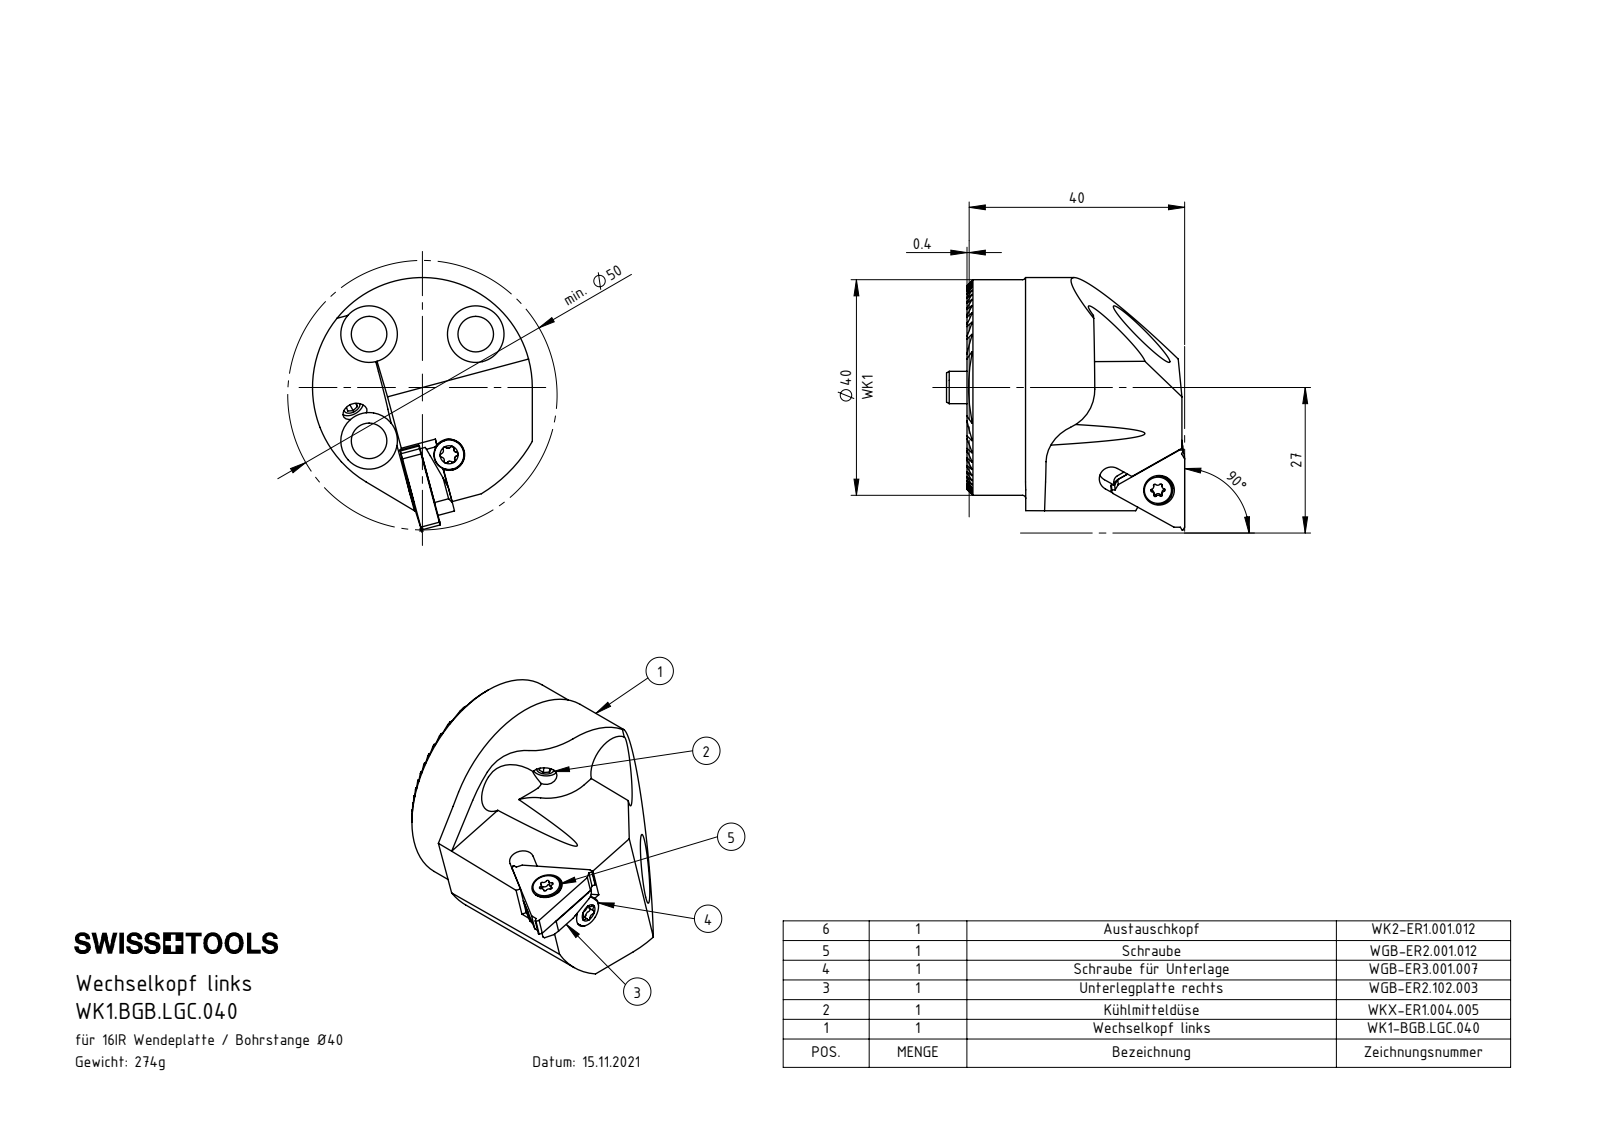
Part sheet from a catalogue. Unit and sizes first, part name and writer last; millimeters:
Units: millimetres
Overall size (bounding box): 47.42 × 44.27 × 42
Round holes (diameter × count): ⌀6.6 ×3, ⌀10.5 ×3, ⌀2.58 ×2, ⌀3.3 ×2, ⌀4 ×2, ⌀1.7 ×1, ⌀3 ×1, ⌀4.02 ×1, ⌀4.2 ×1, ⌀4.5 ×1, ⌀12 ×1
Round bosses / shafts (diameter × count): ⌀5.5 ×2, ⌀4 ×2, ⌀40 ×1, ⌀6 ×1, ⌀3.18 ×1, ⌀3 ×1, ⌀2.78 ×1
Partial cylindrical surfaces — rounded edges, fillets, slot ends (radius × count): R0.12 ×26, R0.23 ×6, R0.34 ×6, R0.57 ×6, R0.57 ×6, R0.1 ×2, R10 ×2, R0.25 ×1
Main face-to-face distances: 1.3, 2.6, 3.9, 12.99, 5.2, 11.69, 9.09, 10.39, 7.79, 6.5
Hole centre spacings: 14, 19.8, 28, 279.88, 279.93
Volume: 35 784 mm³ · Surface area: 12 516 mm²
Bodies: 9 solids, 408 faces (242 planar, 116 cylindrical, 50 other)
Part name (STEP PRODUCT): WGB-ER3.001.007_A; WK1.BGB.LGC.040; WK2-ER1.001.012_A_Fertigbearbeitung; WK1-BGB.LGC.040_B (+5 more)
STEP written by: SolidWorks 2017 (AUTOMOTIVE_DESIGN)
